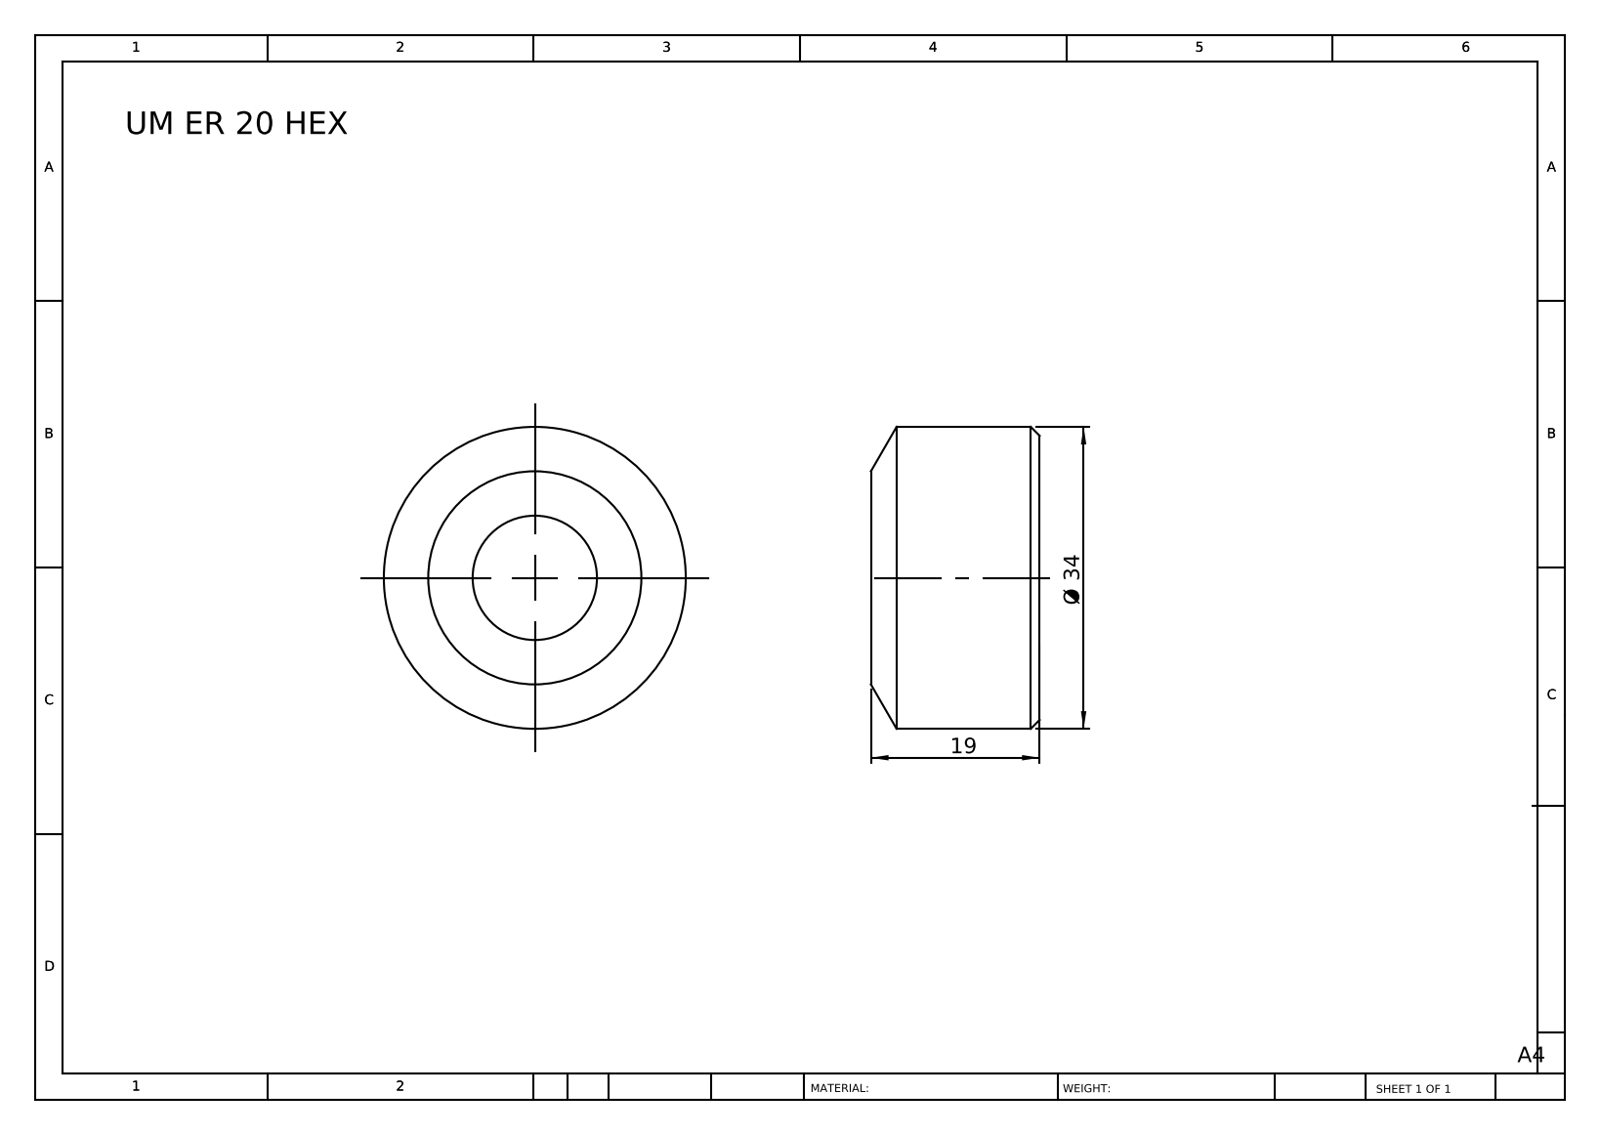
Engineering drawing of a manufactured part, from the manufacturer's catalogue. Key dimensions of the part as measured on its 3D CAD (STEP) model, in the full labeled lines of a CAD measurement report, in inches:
Part name (STEP PRODUCT): UM ER 20 HEX
STEP written by: SolidWorks 2014 (CONFIG_CONTROL_DESIGN)
Units: inches
Bodies: 1 solid, 10 faces (2 planar, 4 cylindrical, 4 other)
Overall size (bounding box): 1.339 × 1.339 × 0.748
Volume: 0.829 in³ · Surface area: 6.31 in²
Round holes (diameter × count): ⌀0.551 ×1
Round bosses / shafts (diameter × count): ⌀1.339 ×1
Main face-to-face distances: 0.748
